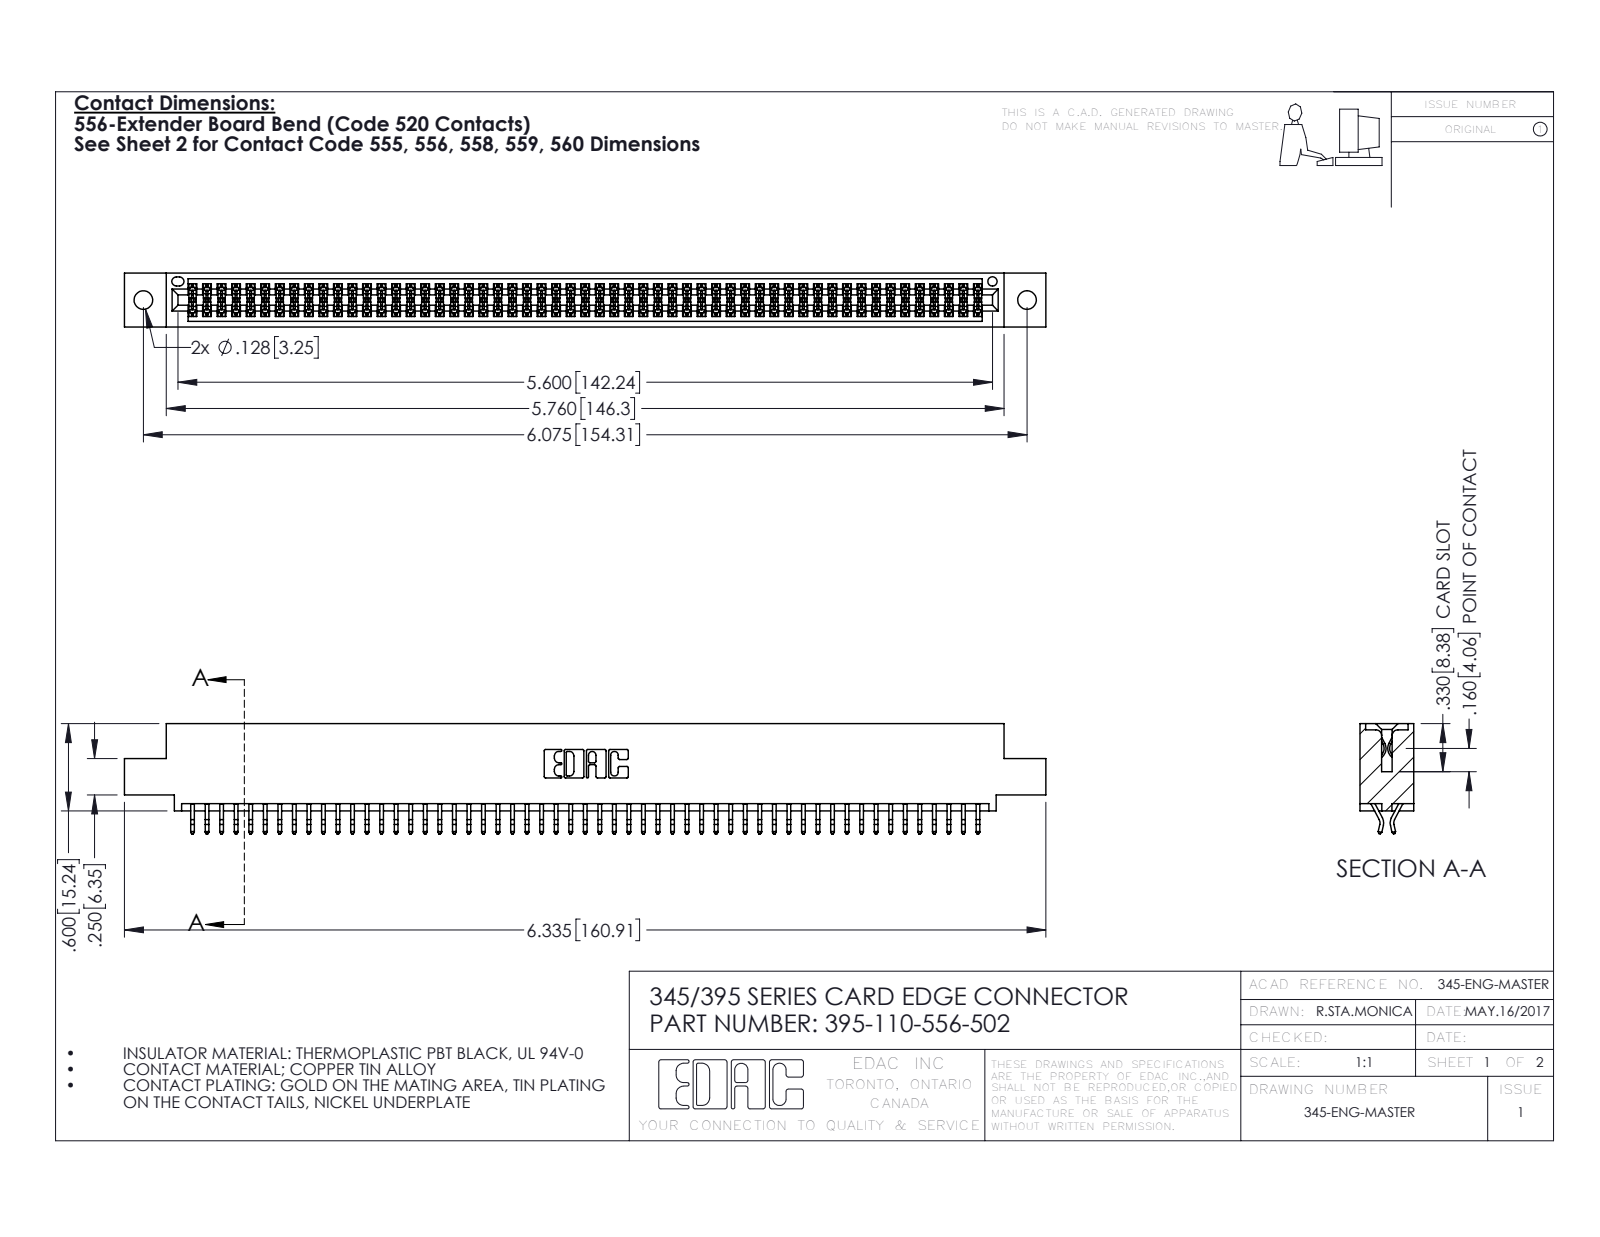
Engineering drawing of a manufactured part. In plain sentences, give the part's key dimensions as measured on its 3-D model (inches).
The part is named "345-292-001_556 Tail; 395-110-556-502; 345 Part_0.110 Offset - 0.128 Dia". Its 3-D file was written by "SolidWorks 2016 (CONFIG_CONTROL_DESIGN)". It is 111 solids with 6290 faces: 4154 planar, 2136 cylindrical and 0 other. Overall it measures 6.335 by 0.757 by 0.37 inches. Its volume is 0.954 cubic inches and its surface area 35.79 square inches. Round holes: 2 of diameter 0.128, 1 of diameter 0.064. Partial cylindrical surfaces (rounded edges, fillets, slot ends): 165 of radius 0.006, 22 of radius 0.01, 6 of radius 0.007, 6 of radius 0.031, 3 of radius 0.026, 2 of radius 0.01, 2 of radius 0.014, 2 of radius 0.019. The main face-to-face distances are 0.298, 0.072, 0.37, 0.2, 0.025, 0.098, 0.272, 0.225, 0.175, 0.149. The hole center spacings are 0.27, 5.839, 6.075.
